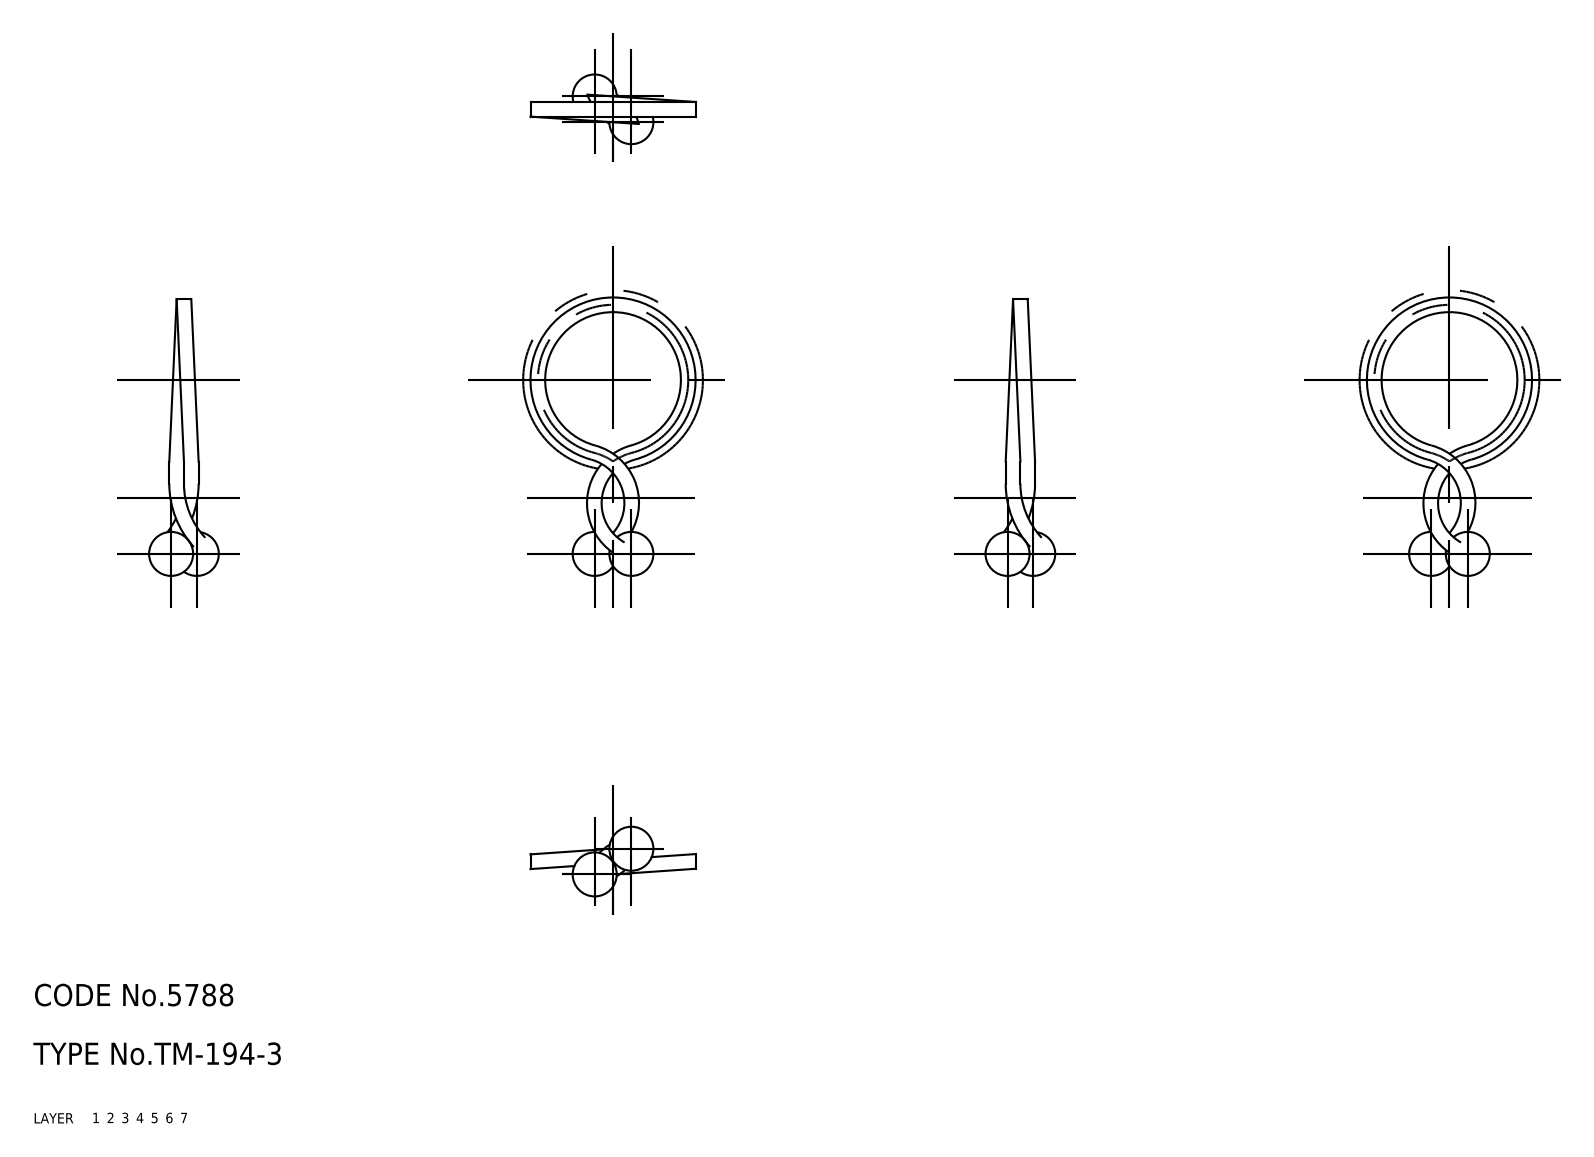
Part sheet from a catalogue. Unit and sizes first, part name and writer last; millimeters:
Units: millimetres
Overall size (bounding box): 37.7 × 22.09 × 10.2
Volume: 588 mm³ · Surface area: 943 mm²
Bodies: 1 solid, 18 faces (0 planar, 0 cylindrical, 18 other)
Part name (STEP PRODUCT): clip
STEP written by: CADfix (AUTOMOTIVE_DESIGN)
